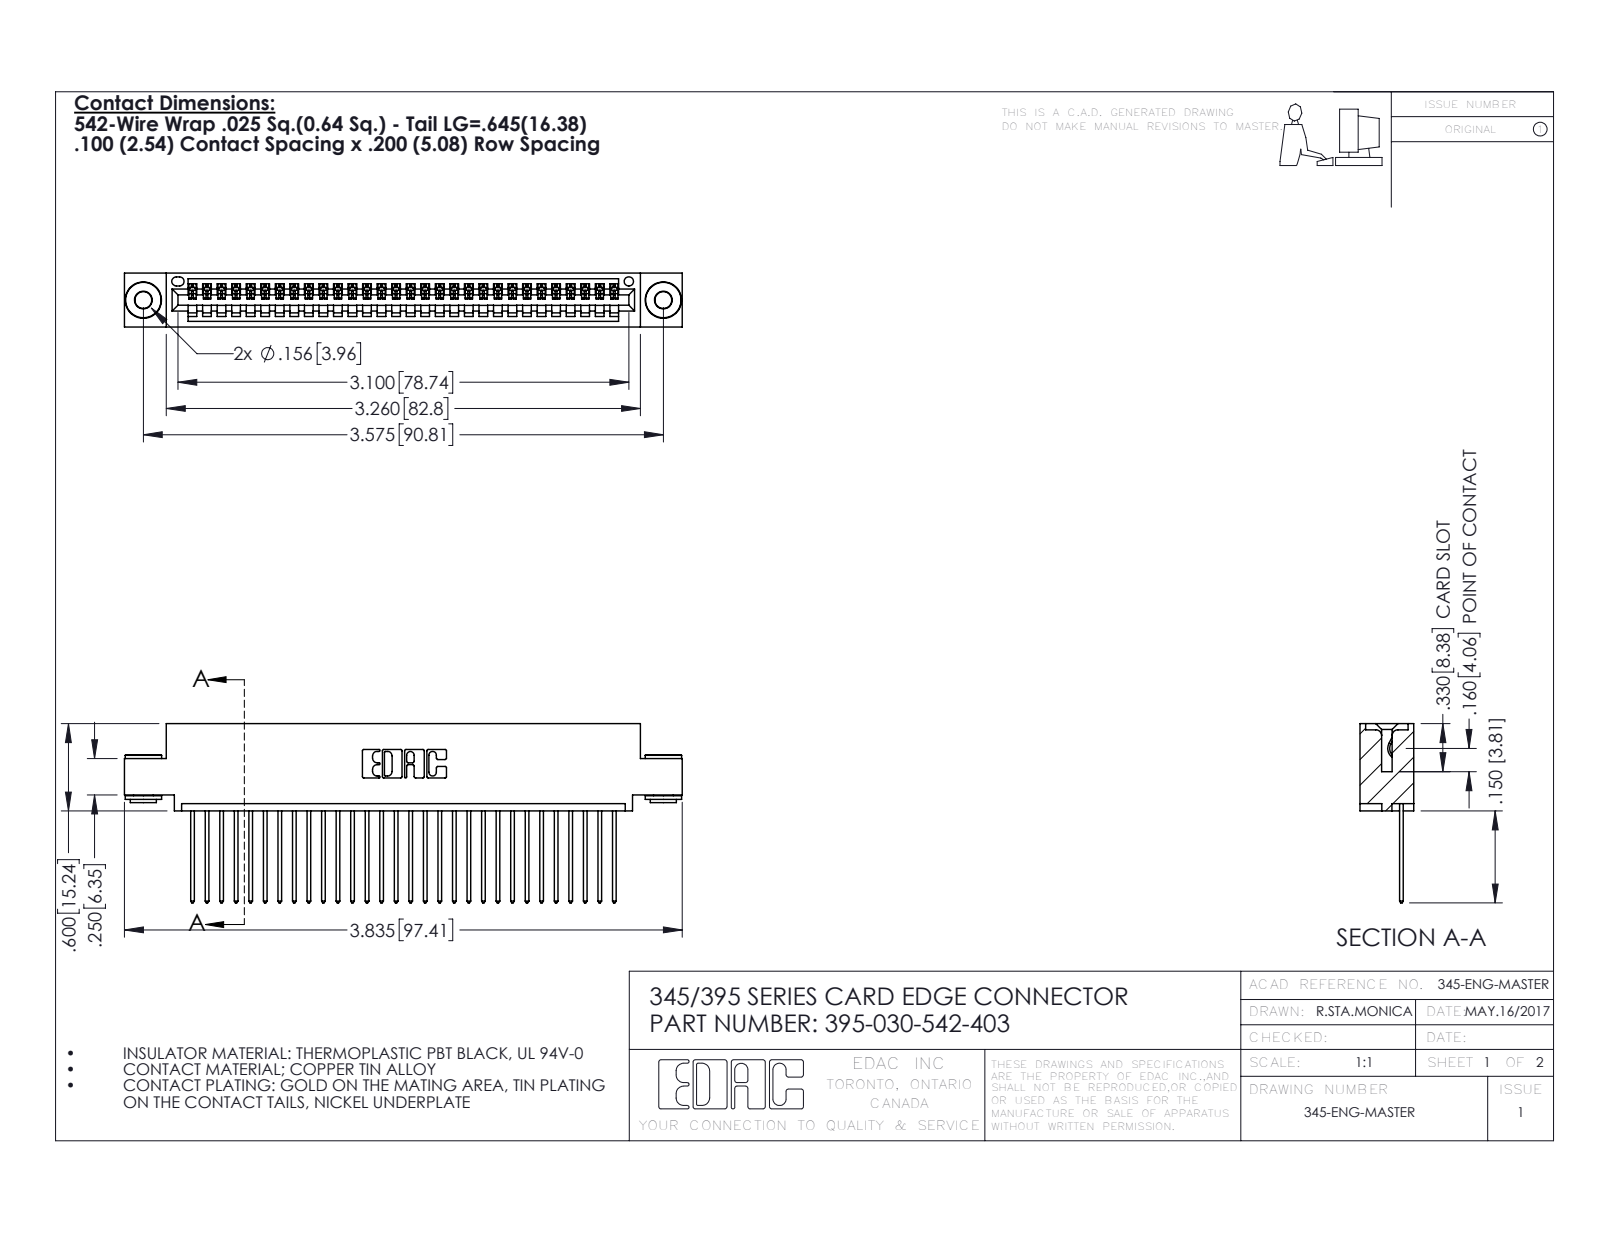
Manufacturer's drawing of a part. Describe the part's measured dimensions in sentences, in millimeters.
The part is named "345 Part_0.110 Offset - 0.156 Dia-TH; 395-030-542-403; 345-250-002_345-250-002-102; 345-292-001_345-293-142". Its 3-D file was written by "SolidWorks 2016 (CONFIG_CONTROL_DESIGN)". It is 33 solids with 1908 faces: 1294 planar, 606 cylindrical and 8 other. Overall it measures 97.4 by 31.3 by 9.4 millimeters. Its volume is 9 160 cubic millimeters and its surface area 12 740 square millimeters. Round holes: 2 of diameter 2.9, 2 of diameter 4, 1 of diameter 1.6. Round bosses or shafts: 2 of diameter 6.4, 2 of diameter 4.6, 2 of diameter 3.5. Partial cylindrical surfaces (rounded edges, fillets, slot ends): 60 of radius 0.2, 60 of radius 0.3, 22 of radius 0.3, 6 of radius 0.2, 6 of radius 0.8, 3 of radius 0.7, 2 of radius 0.8, 2 of radius 1. The main face-to-face distances are 1.8, 7.6, 0.6, 9.4, 2.5, 6.9, 5.1, 5.7, 3.8, 1.8. The hole center spacings are 6.9, 84.8, 90.8.
